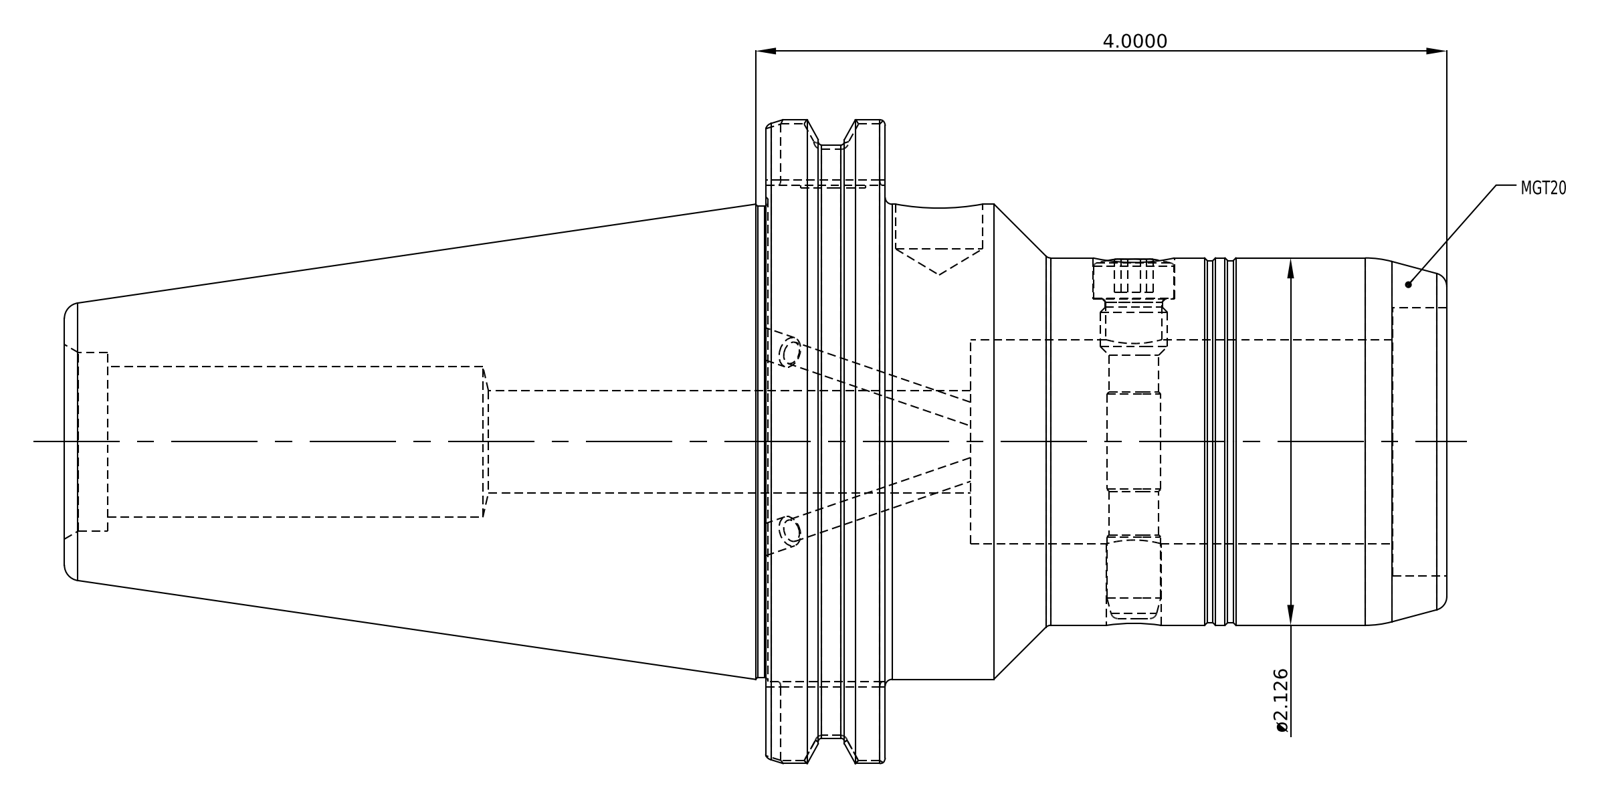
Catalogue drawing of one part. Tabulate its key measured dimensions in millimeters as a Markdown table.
| quantity | value |
| --- | --- |
| part name | BCV50-MGT20-4; MGT20SS |
| STEP written by | SolidWorks 2015 (AUTOMOTIVE_DESIGN) |
| units | millimeters |
| bodies | 2 solids, 220 faces (51 planar, 74 cylindrical, 95 other) |
| overall size | 203.2 × 98.42 × 94.62 |
| volume | 496 294 mm³ |
| surface area | 67 251 mm² |
| round holes (diameter × count) | 3.3 × 2, 4.5 × 2, 8 × 1, 8.3 × 1, 9.5 × 1, 12 × 1, 12.7 × 1, 15 × 1, 22.2 × 1, 26.2 × 1, 30 × 1, 39.4 × 1 |
| round bosses / shafts (diameter × count) | 98.42 × 1, 91.29 × 1, 69.85 × 1, 69.25 × 1, 54 × 1, 53.2 × 1, 11.8 × 1, 9.9 × 1 |
| partial cylindrical surfaces (radius × count) | 0.76 × 12 |
| main face-to-face distances | 17.55, 92.1, 74.55, 30.1, 12.55, 62, 100.1, 82.55, 70, 8 |
| hole center spacings | 15.6, 28.63, 44.23 |
